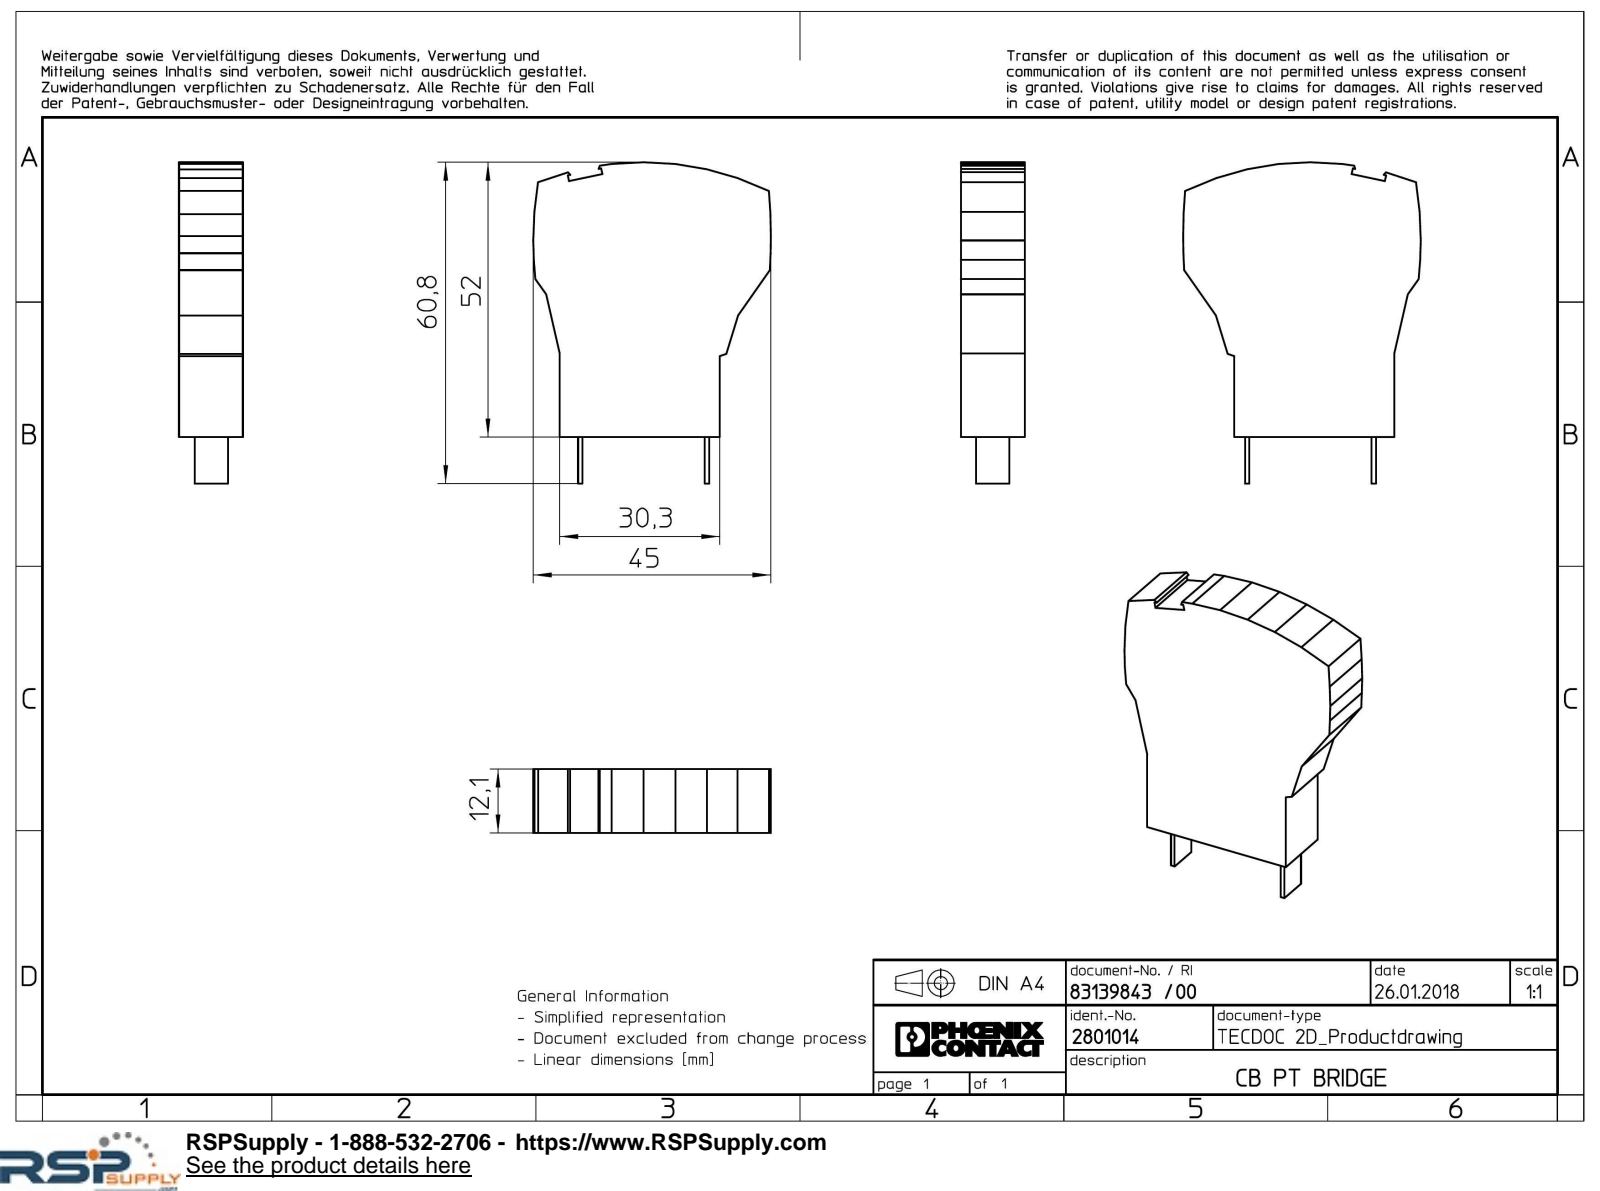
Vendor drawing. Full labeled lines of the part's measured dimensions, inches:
Part name (STEP PRODUCT): CB_PT_BRIDGE-select
STEP written by: Creo Elements/Direct Modeling 18.1I 14-Aug-2016 (C) Parametric Technology GmbH (AUTOMOTIVE_DESIGN)
Units: inches
Bodies: 1 solid, 42 faces (42 planar, 0 cylindrical, 0 other)
Overall size (bounding box): 2.394 × 1.772 × 0.476
Volume: 1.401 in³ · Surface area: 9.604 in²
Main face-to-face distances: 0.476, 1.193, 0.031, 0.945, 0.079, 1.055, 0.976, 1.114, 0.138, 0.11
